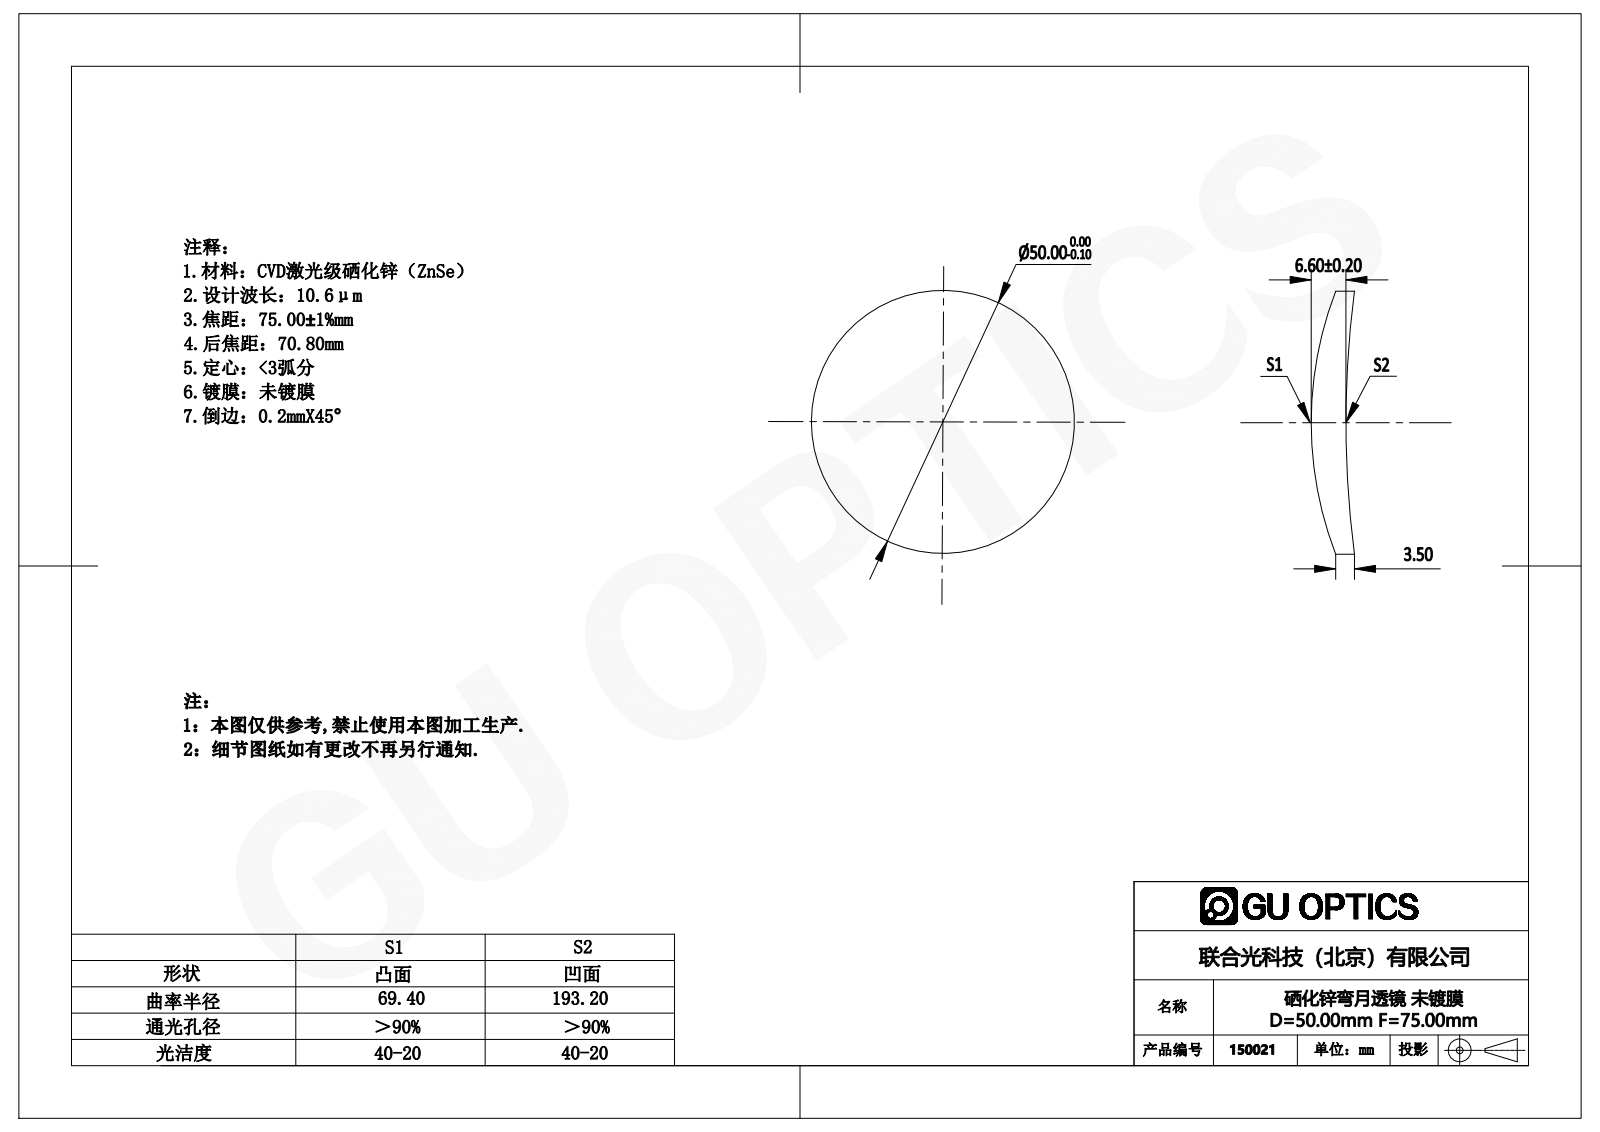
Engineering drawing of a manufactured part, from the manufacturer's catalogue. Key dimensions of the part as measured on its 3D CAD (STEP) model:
Part name (STEP PRODUCT): 150021
STEP written by: SolidWorks 2016 (AUTOMOTIVE_DESIGN)
Units: millimetres
Bodies: 1 solid, 6 faces (0 planar, 2 cylindrical, 4 other)
Overall size (bounding box): 50 × 50 × 8.22
Volume: 10 030 mm³ · Surface area: 4 563 mm²
Round bosses / shafts (diameter × count): ⌀50 ×1
